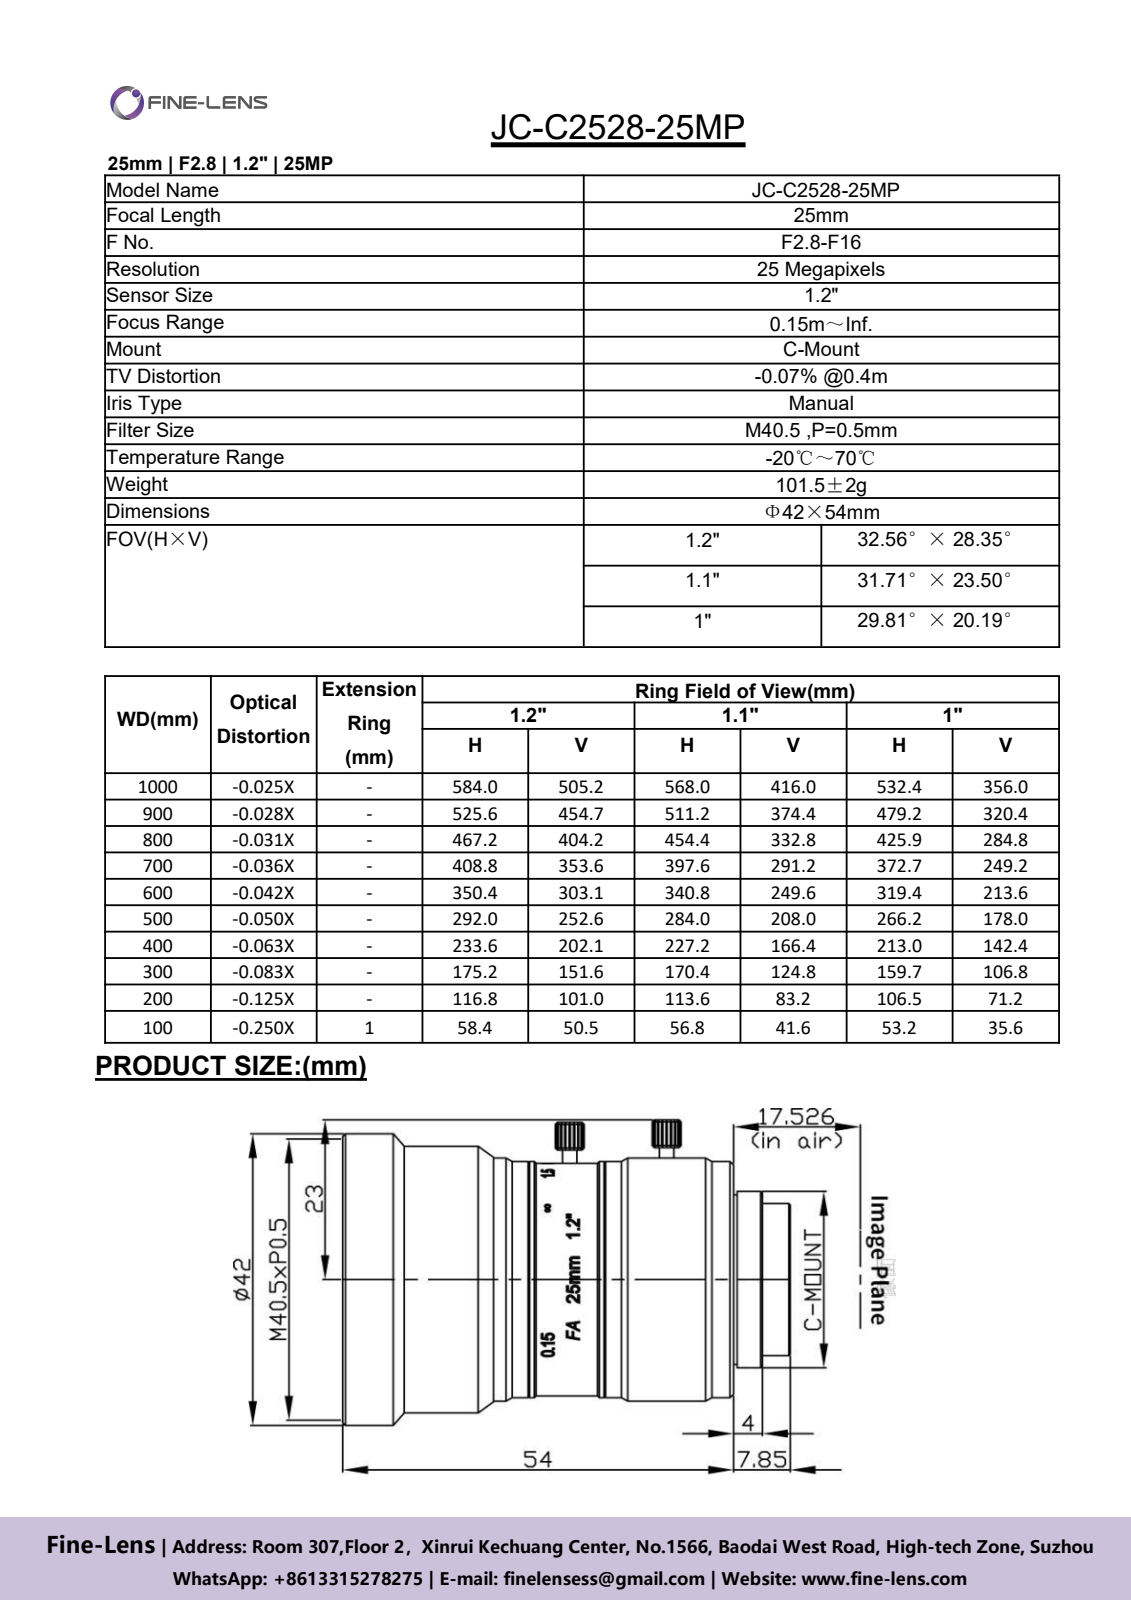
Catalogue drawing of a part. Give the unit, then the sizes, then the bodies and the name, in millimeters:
Units: millimetres
Overall size (bounding box): 61.89 × 44 × 42
Round holes (diameter × count): ⌀2 ×4, ⌀1.7 ×3, ⌀3 ×1, ⌀17.26 ×1, ⌀17.37 ×1, ⌀17.6 ×1, ⌀18 ×1, ⌀18.2 ×1, ⌀18.4 ×1, ⌀18.6 ×1, ⌀19 ×1, ⌀19.9 ×1
Round bosses / shafts (diameter × count): ⌀2.3 ×3, ⌀1.6 ×3, ⌀42 ×1, ⌀38.4 ×1, ⌀35 ×1, ⌀34 ×1, ⌀33.8 ×1, ⌀33.5 ×1
Partial cylindrical surfaces — rounded edges, fillets, slot ends (radius × count): R2 ×2, R16.74 ×1, R16.99 ×1
Main face-to-face distances: 51.55, 2.5, 44.9, 4, 22.6, 28.95, 10.65, 22.28, 0.32, 29.27
Hole centre spacings: 14.35, 24.86, 10.15, 24.85
Volume: 43 089 mm³ · Surface area: 17 426 mm²
Bodies: 8 solids, 1047 faces (426 planar, 236 cylindrical, 385 other)
Part name (STEP PRODUCT): F25mm; SNZFS-M1.6-3; LB-3; 锁紧钉1
STEP written by: SolidWorks 2022 (CONFIG_CONTROL_DESIGN)
